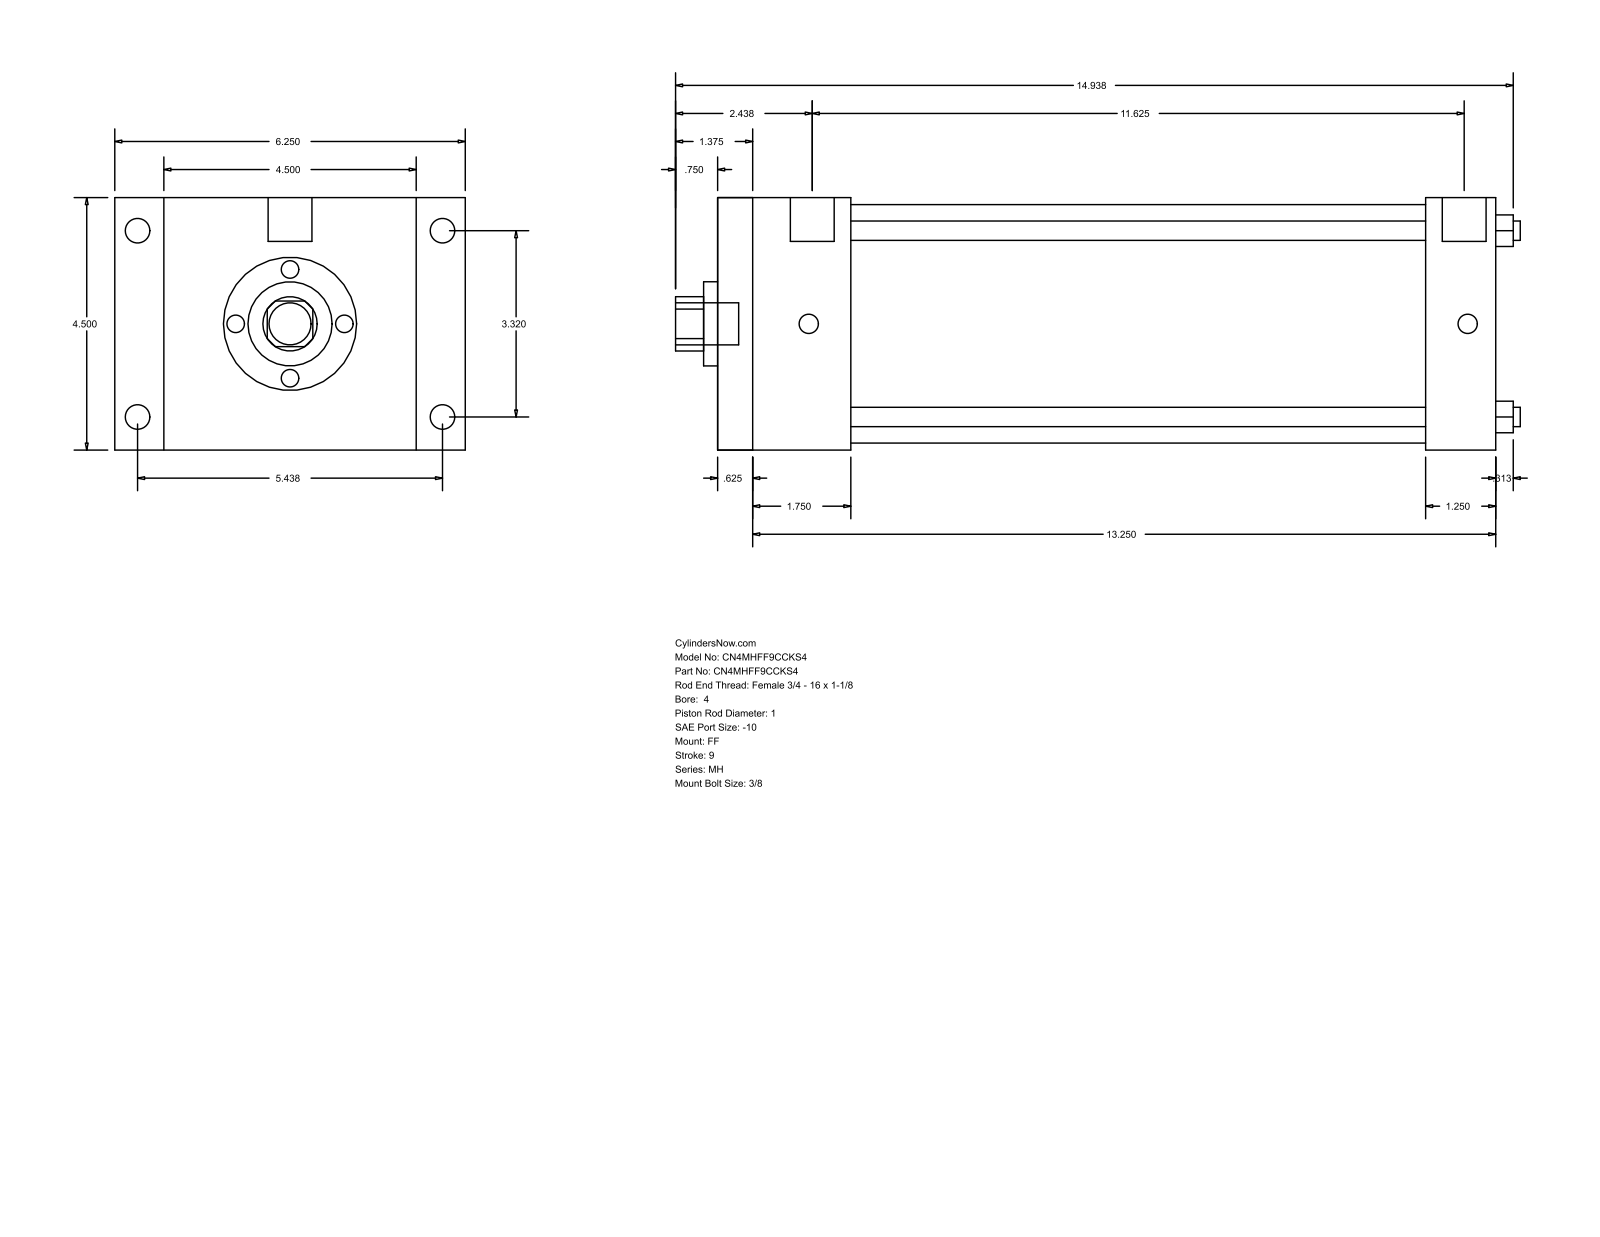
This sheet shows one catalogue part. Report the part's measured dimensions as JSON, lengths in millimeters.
{"part_name": "MH_FF__0400_1", "step_written_by": "GSSL Pune (CONFIG_CONTROL_DESIGN)", "units": "millimeters", "bodies": {"solids": 0, "faces": 92, "planar": 64, "cylindrical": 28, "other": 0}, "overall_size": [382.59, 158.75, 114.3], "round_holes": [[8.76, 4], [25.4, 1], [38.1, 1], [107.95, 1]], "round_bosses_or_shafts": [[11.13, 4], [8.73, 4], [19.84, 2], [19.05, 1]], "partial_cylinders_radius": [[12.29, 1]], "face_to_face_distances": [114.3, 352.43, 15.87, 336.56, 60.33, 44.46, 292.1, 320.68, 304.81, 260.35], "hole_center_spacings": [59.62, 84.32, 119.25]}
